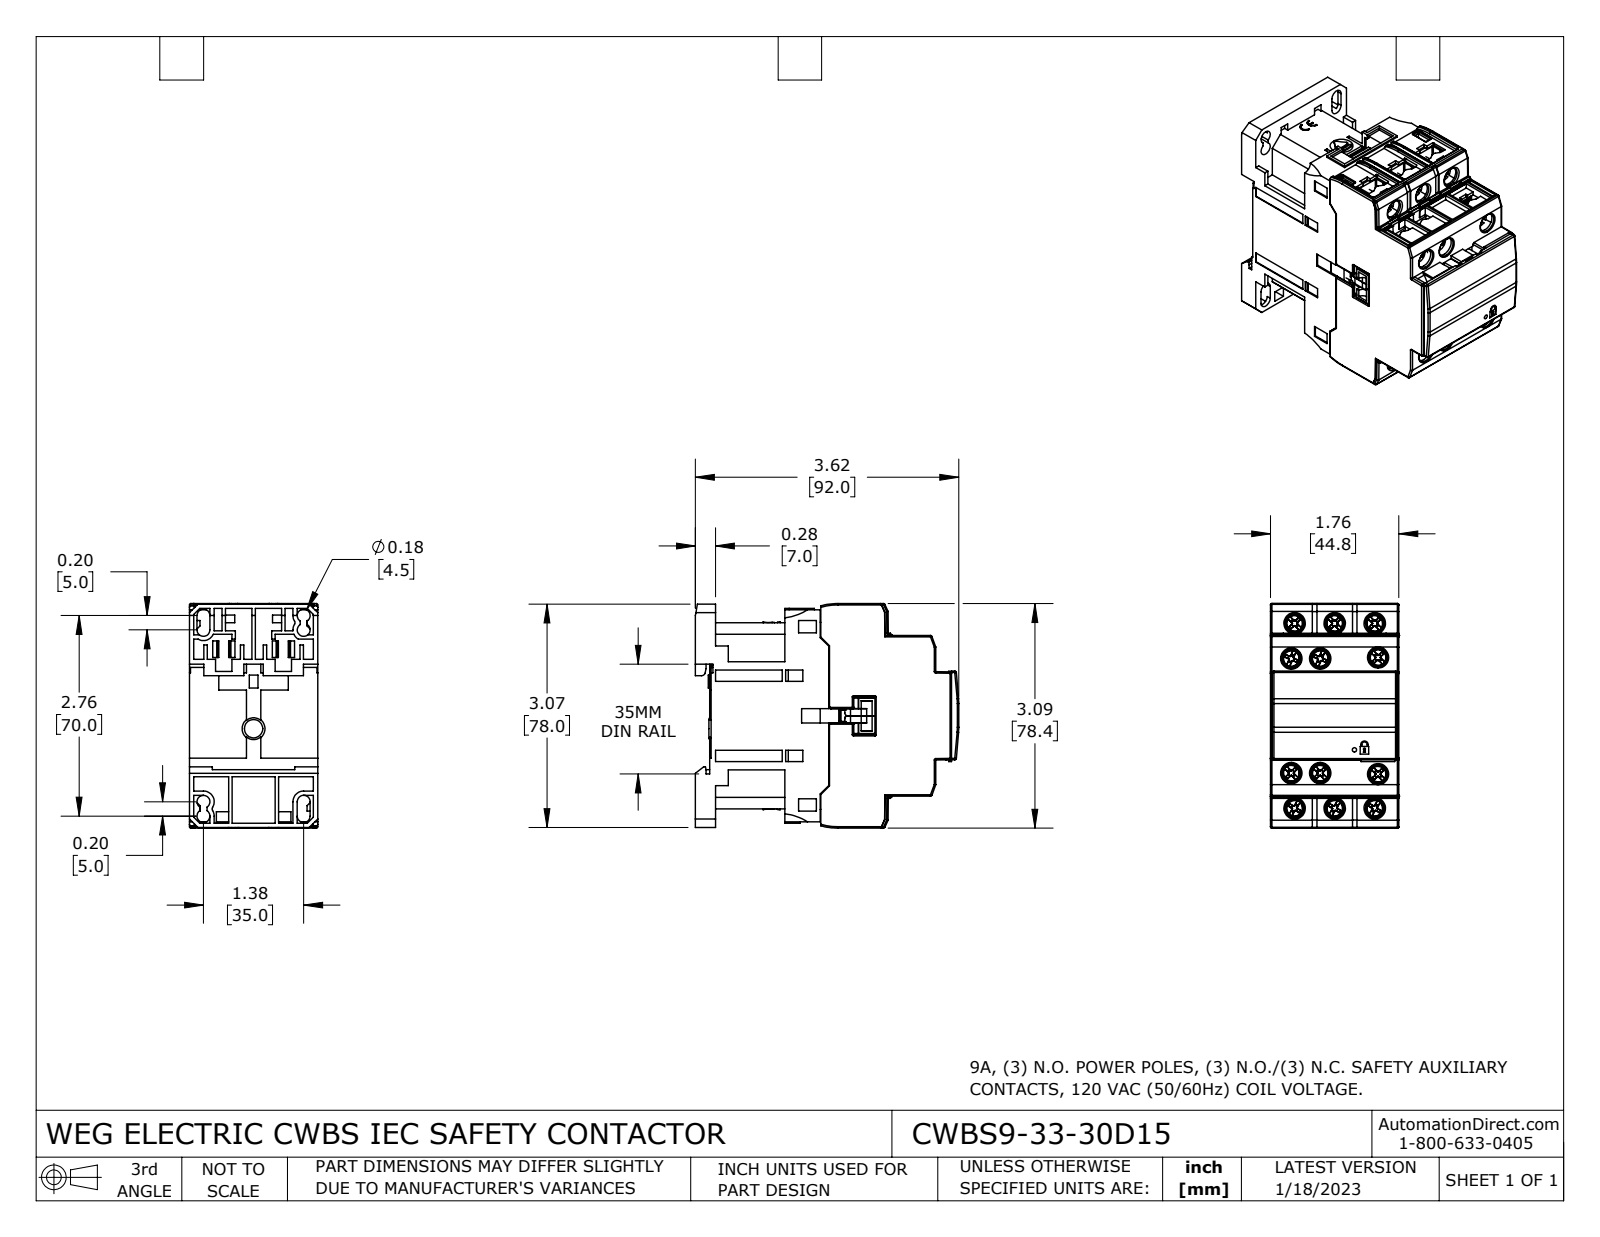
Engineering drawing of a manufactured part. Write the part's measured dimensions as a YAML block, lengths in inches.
part_name: "CWBS9-33-30D15"
step_written_by: "SolidWorks 2021 (CONFIG_CONTROL_DESIGN)"
units: inches
bodies: {solids: 45, faces: 3295, planar: 2311, cylindrical: 624, other: 360}
overall_size: [3.62, 3.087, 1.764]
volume: 13.51
surface_area: 120.4
round_holes:
  - {diameter: 0.124, count: 12}
  - {diameter: 0.256, count: 6}
  - {diameter: 0.177, count: 4}
  - {diameter: 0.059, count: 1}
round_bosses_or_shafts:
  - {diameter: 0.169, count: 12}
  - {diameter: 0.138, count: 12}
  - {diameter: 0.107, count: 8}
  - {diameter: 0.107, count: 4}
partial_cylinders:
  - {radius: 0.02, count: 139}
  - {radius: 0.012, count: 52}
  - {radius: 0.071, count: 24}
  - {radius: 0.964, count: 24}
  - {radius: 2.128, count: 24}
  - {radius: 0.016, count: 20}
  - {radius: 0.039, count: 19}
  - {radius: 0.106, count: 11}
face_to_face_distances: [1.764, 0.047, 1.717, 3.305, 1.754, 1.551, 0.276, 0.022, 1.776, 1.53]
hole_center_spacings: [0.551, 1.102, 0.197, 0.398, 0.795, 1.193, 1.341, 1.575]
